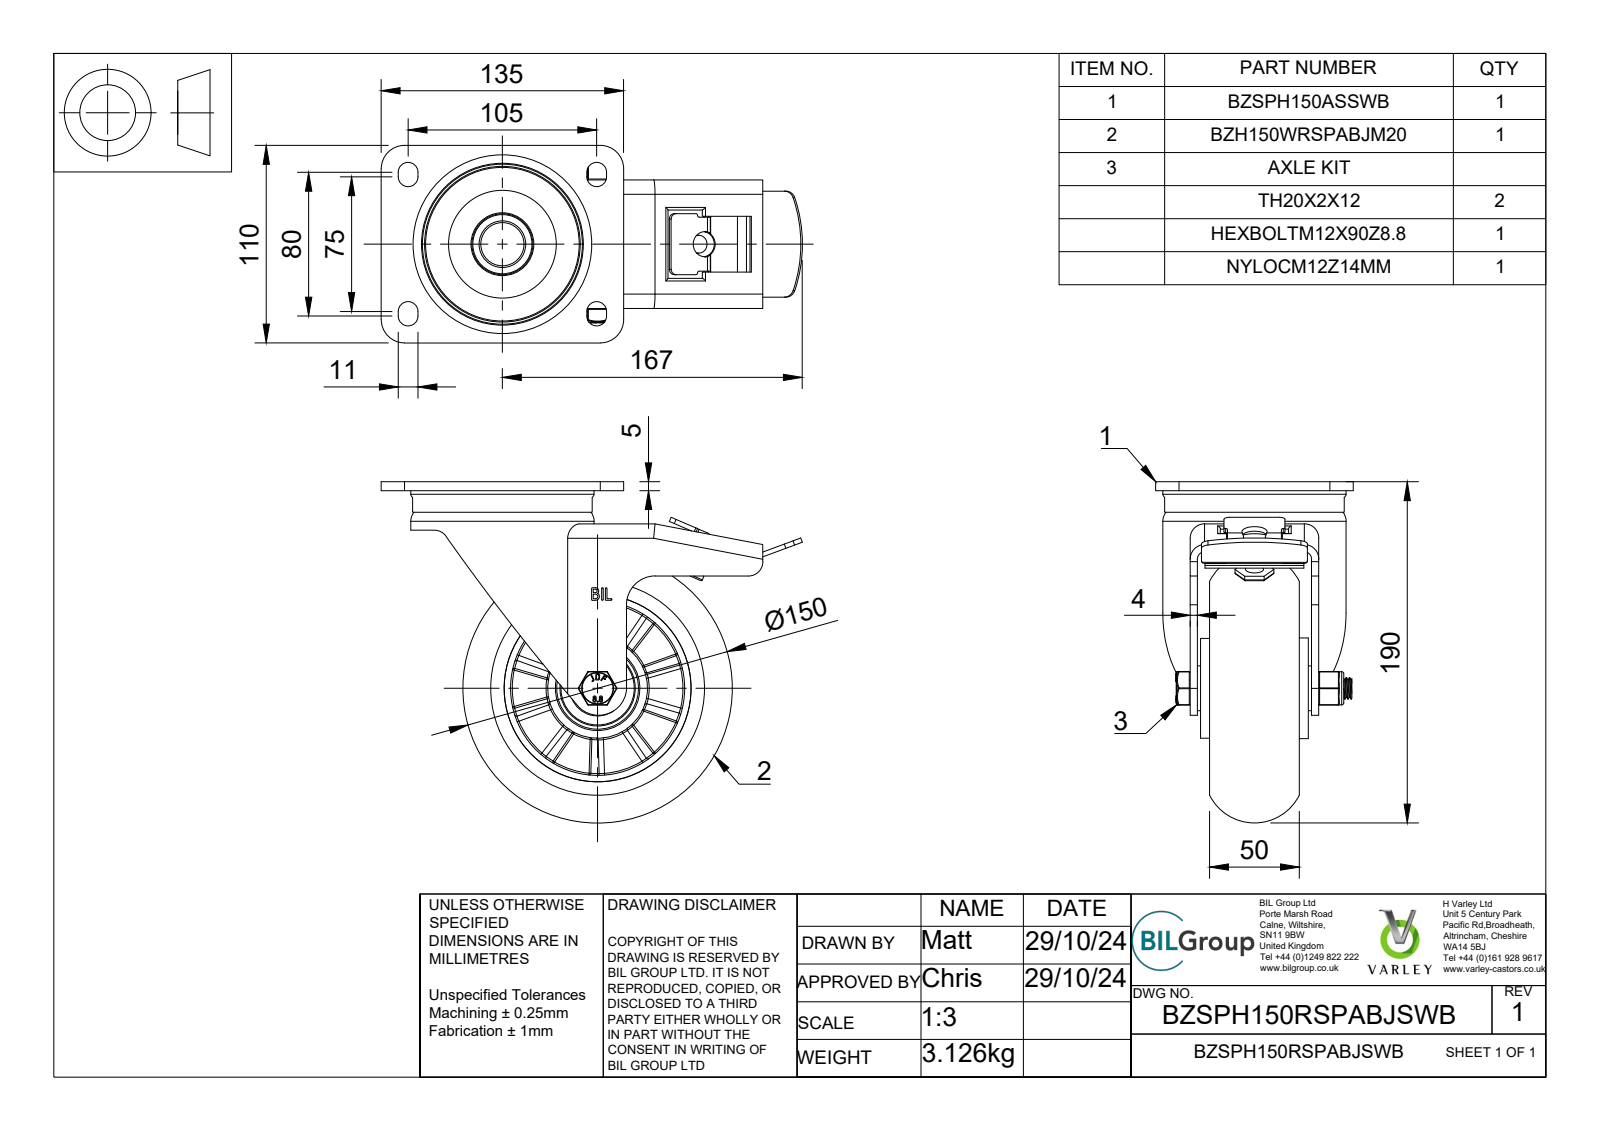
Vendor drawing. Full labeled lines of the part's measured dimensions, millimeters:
Part name (STEP PRODUCT): BZSPH150RSPABJSWB v3; BZSPH150ASSWB v1; ZINC PLATED, PRESSED STEEL TOP PLATE; ZINC PLATED, PRESSED STEEL TOP PLATE Geometry (+6 more)
STEP written by: Autodesk Translation Framework v13.20.0.188 (AUTOMOTIVE_DESIGN)
Units: millimetres
Bodies: 158 solids, 1714 faces (599 planar, 301 cylindrical, 814 other)
Overall size (bounding box): 234.5 × 190 × 110
Volume: 823 298 mm³ · Surface area: 324 784 mm²
Round holes (diameter × count): ⌀10 ×2, ⌀14 ×2, ⌀12 ×1, ⌀12.2 ×1, ⌀20 ×1, ⌀28.5 ×1, ⌀30.8 ×1, ⌀40 ×1, ⌀40.3 ×1, ⌀40.5 ×1, ⌀42 ×1, ⌀47 ×1
Round bosses / shafts (diameter × count): ⌀24 ×2, ⌀102 ×1, ⌀100 ×1, ⌀74 ×1, ⌀72 ×1, ⌀56 ×1, ⌀55.5 ×1, ⌀40.8 ×1
Partial cylindrical surfaces — rounded edges, fillets, slot ends (radius × count): R0.5 ×20, R1 ×10, R1.5 ×10, R5.5 ×10, R4 ×7, R0.75 ×6, R2 ×6, R8 ×6
Main face-to-face distances: 4, 9, 5, 67.5, 14, 1, 10.75, 60.75, 6.75, 56.75
